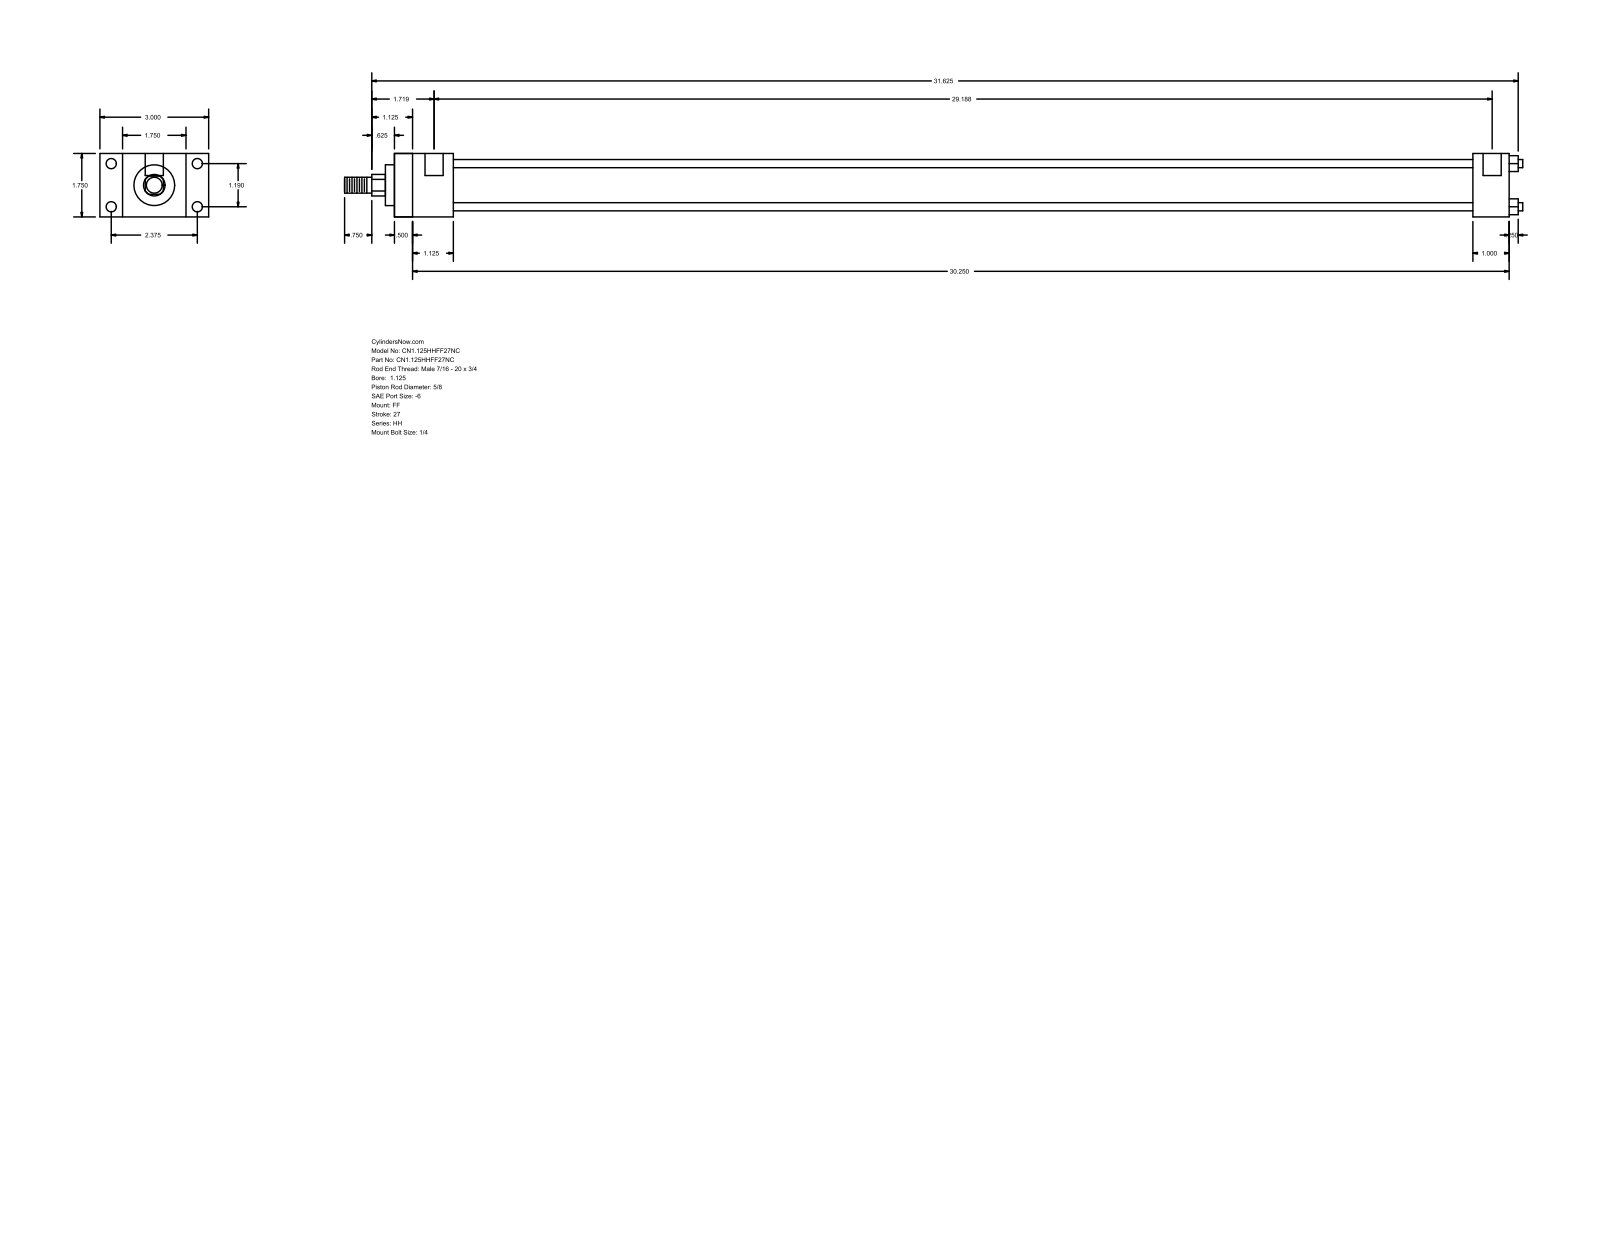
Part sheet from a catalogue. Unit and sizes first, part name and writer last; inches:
Units: inches
Overall size (bounding box): 32.5 × 3 × 1.75
Round holes (diameter × count): ⌀0.219 ×4, ⌀0.281 ×4, ⌀0.5 ×2
Round bosses / shafts (diameter × count): ⌀0.225 ×4, ⌀1.375 ×1, ⌀1.125 ×1, ⌀0.625 ×1, ⌀0.437 ×1
Partial cylindrical surfaces — rounded edges, fillets, slot ends (radius × count): R0.297 ×1
Main face-to-face distances: 1.75, 30.75, 0.625, 0.5, 30.25, 1.125, 2.375, 1, 1.625, 29.75
Hole centre spacings: 1.19, 2.375, 2.656, 29.063, 0.125, 29.187
Bodies: 0 solids, 92 faces (64 planar, 28 cylindrical, 0 other)
Part name (STEP PRODUCT): HH_FF__0112_0.625
STEP written by: GSSL Pune (CONFIG_CONTROL_DESIGN)
